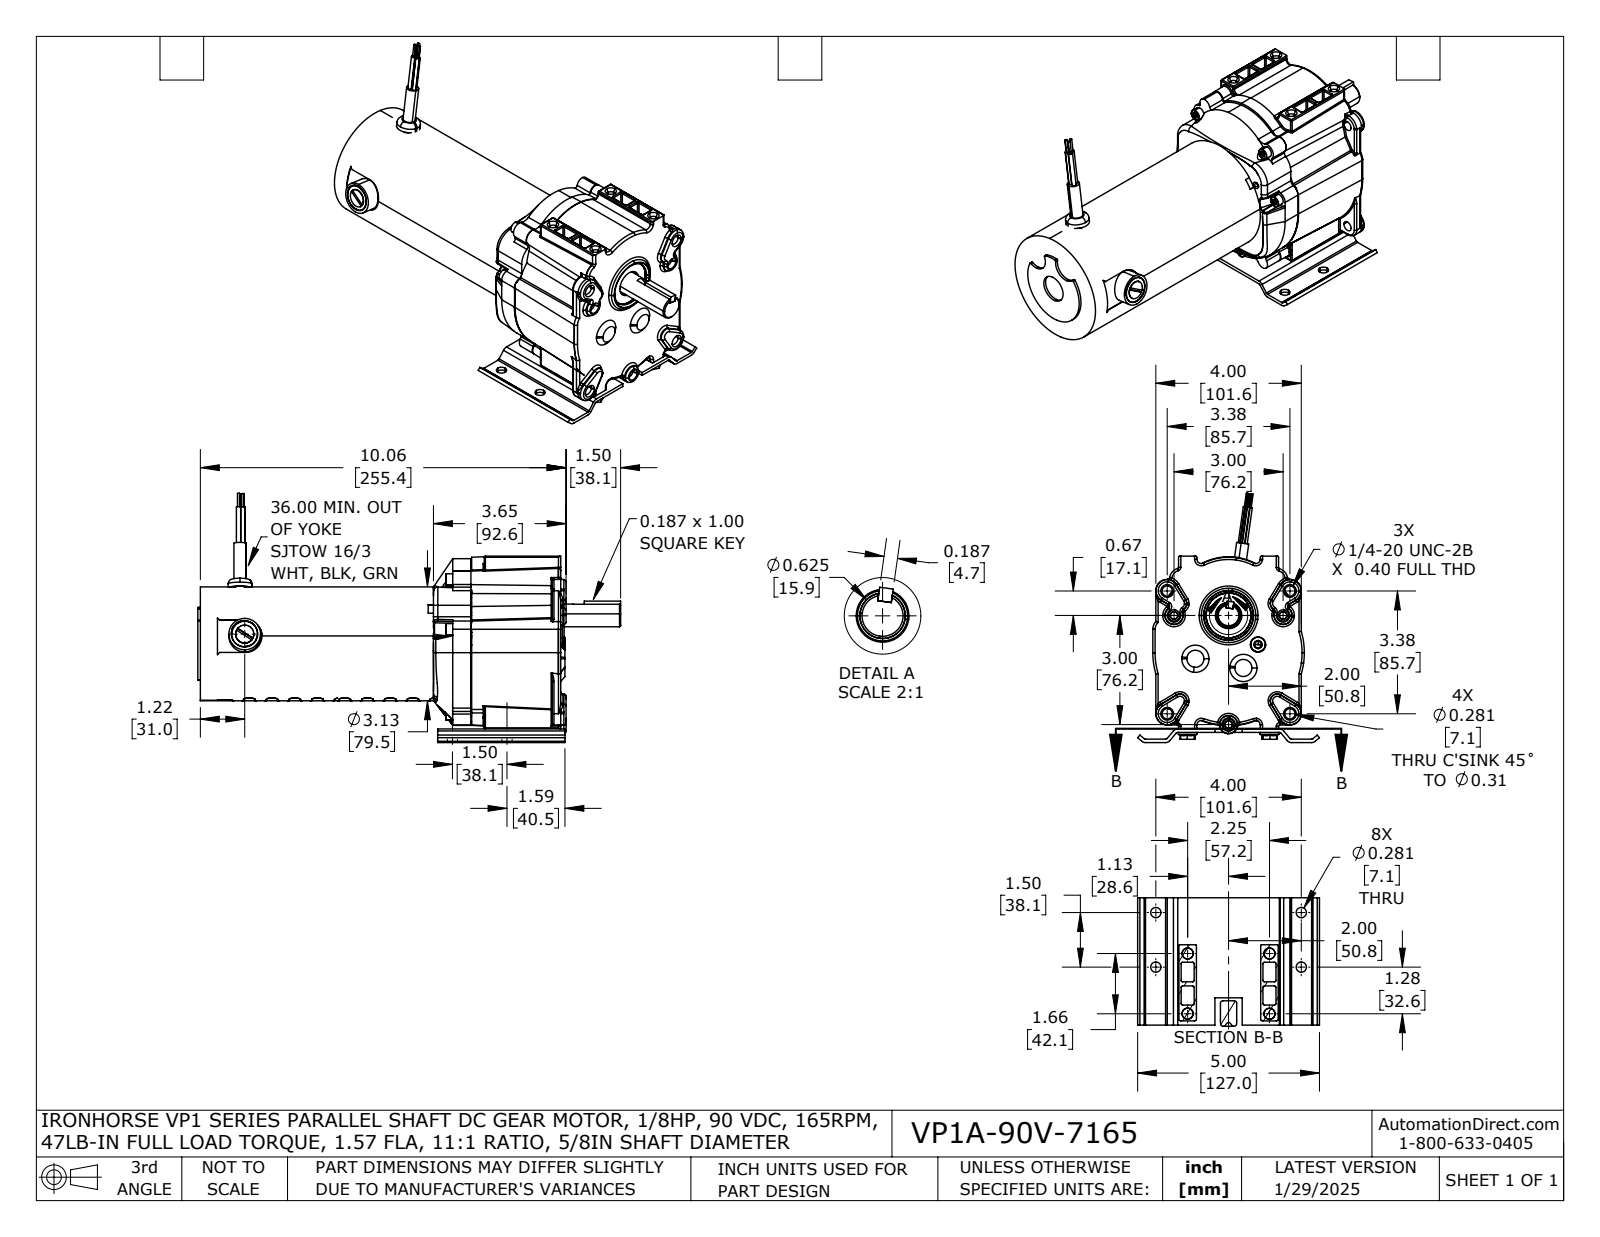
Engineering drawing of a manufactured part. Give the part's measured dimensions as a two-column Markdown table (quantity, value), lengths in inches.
| quantity | value |
| --- | --- |
| part name | VP1A-90V-7165 |
| STEP written by | SolidWorks 2024 (AUTOMOTIVE_DESIGN) |
| units | inches |
| bodies | 10 solids, 2472 faces (654 planar, 701 cylindrical, 1117 other) |
| overall size | 11.627 × 6.854 × 5 |
| volume | 98.93 in³ |
| surface area | 345.4 in² |
| round holes (diameter × count) | 0.281 × 12, 0.218 × 5, 0.159 × 3, 0.207 × 3, 0.135 × 2, 0.166 × 2, 0.204 × 2, 0.397 × 2, 0.688 × 2, 0.875 × 2, 0.75 × 1, 0.813 × 1 |
| round bosses / shafts (diameter × count) | 0.307 × 5, 0.19 × 5, 0.51 × 4, 0.3 × 4, 0.12 × 3, 0.06 × 3, 0.873 × 2, 0.733 × 2 |
| partial cylindrical surfaces (radius × count) | 0.03 × 52, 0.031 × 38, 0.062 × 23, 0.12 × 18, 0.156 × 18, 0.19 × 10, 0.151 × 9, 0.161 × 9 |
| main face-to-face distances | 0.095, 2.449, 3.5, 1.051, 9.44, 6.991, 5.94, 0.47, 6.97, 9.91 |
| hole center spacings | 1.5, 3.375, 1.691, 0.492, 0.698, 1.224, 1.426, 1.552 |
